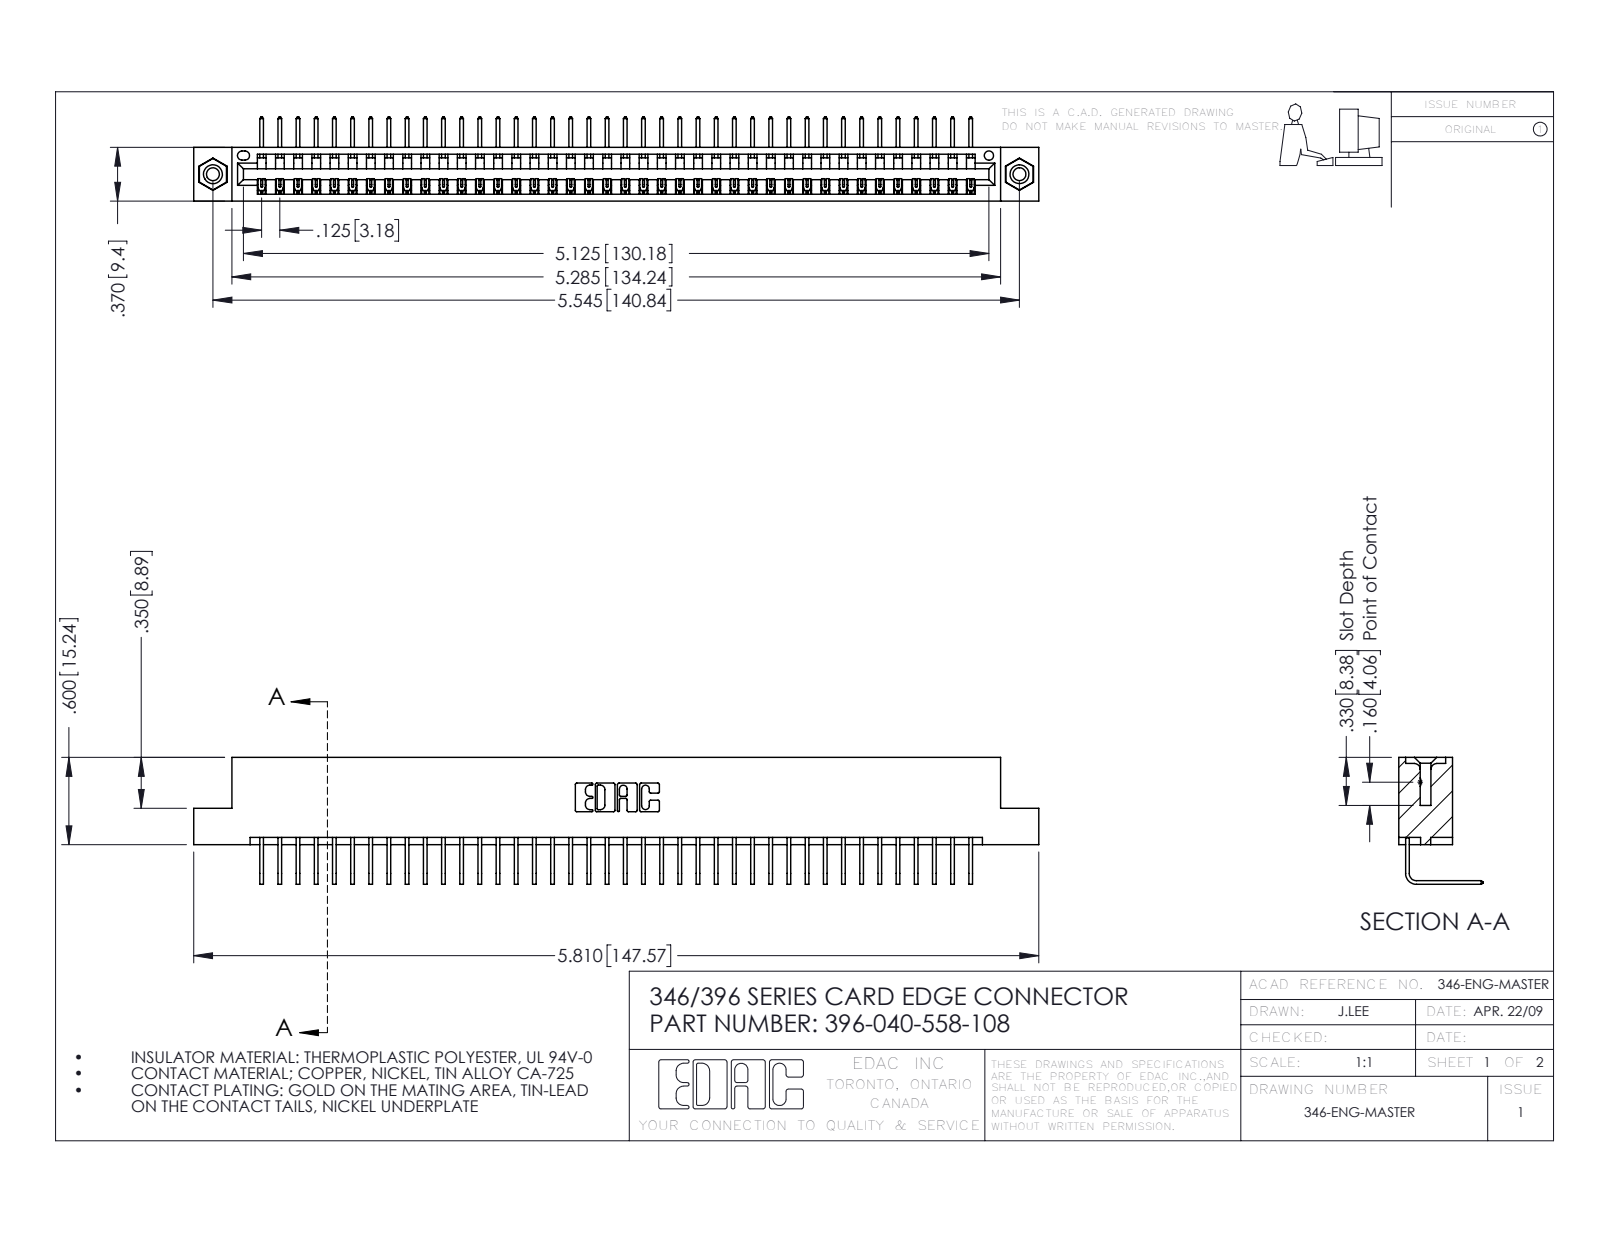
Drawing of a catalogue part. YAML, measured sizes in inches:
part_name: "345-292-001_558 Tail - 2; 396-040-558-108; 346 Part_Flush Mounting Lugs - 0.156 Dia-TI; 345-250-001_345-250-003-102"
step_written_by: "SolidWorks 2016 (CONFIG_CONTROL_DESIGN)"
units: inches
bodies: {solids: 43, faces: 2582, planar: 1788, cylindrical: 778, other: 16}
overall_size: [5.81, 0.873, 0.58]
volume: 0.869
surface_area: 28.82
round_holes:
  - {diameter: 0.089, count: 2}
  - {diameter: 0.125, count: 2}
  - {diameter: 0.156, count: 2}
  - {diameter: 0.064, count: 1}
round_bosses_or_shafts:
  - {diameter: 0.155, count: 2}
partial_cylinders:
  - {radius: 0.006, count: 80}
  - {radius: 0.01, count: 22}
  - {radius: 0.007, count: 6}
  - {radius: 0.031, count: 6}
  - {radius: 0.026, count: 3}
  - {radius: 0.031, count: 2}
  - {radius: 0.04, count: 2}
  - {radius: 0.014, count: 1}
face_to_face_distances: [0.322, 0.048, 0.37, 0.25, 0.298, 0.025, 0.072, 0.148, 0.222, 0.1]
hole_center_spacings: [0.246, 5.336, 5.545]
